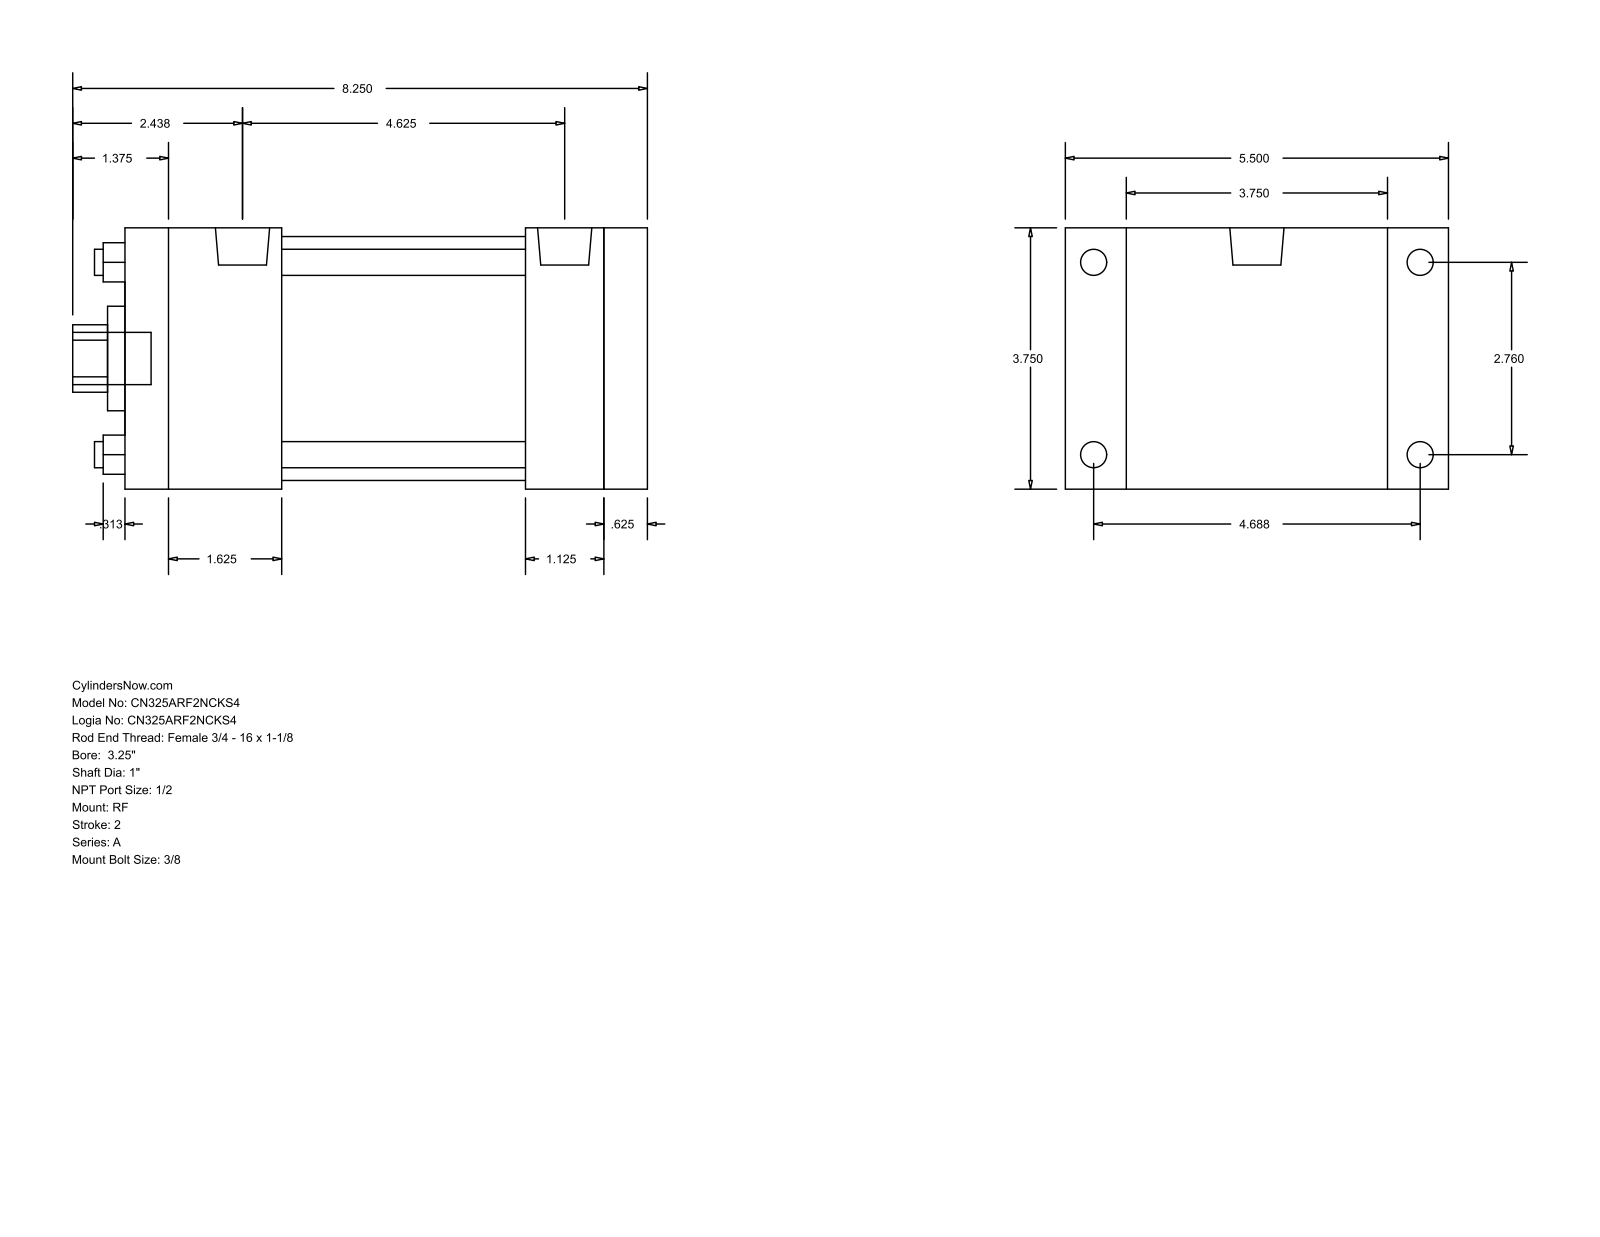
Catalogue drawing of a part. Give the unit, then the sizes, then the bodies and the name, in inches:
Units: inches
Overall size (bounding box): 8.25 × 5.5 × 3.75
Round holes (diameter × count): ⌀0.375 ×4, ⌀1 ×1, ⌀1.5 ×1, ⌀3.5 ×1
Round bosses / shafts (diameter × count): ⌀0.375 ×4, ⌀0.344 ×4, ⌀0.778 ×2, ⌀0.75 ×1
Partial cylindrical surfaces — rounded edges, fillets, slot ends (radius × count): R0.484 ×1
Main face-to-face distances: 3.75, 7.5, 0.625, 6.875, 0.875, 4.625, 5.75, 1.125, 1.75, 2.25
Hole centre spacings: 1.952, 2.76, 3.903
Bodies: 0 solids, 92 faces (64 planar, 28 cylindrical, 0 other)
Part name (STEP PRODUCT): A_RF__0325_1
STEP written by: GSSL Pune (CONFIG_CONTROL_DESIGN)
